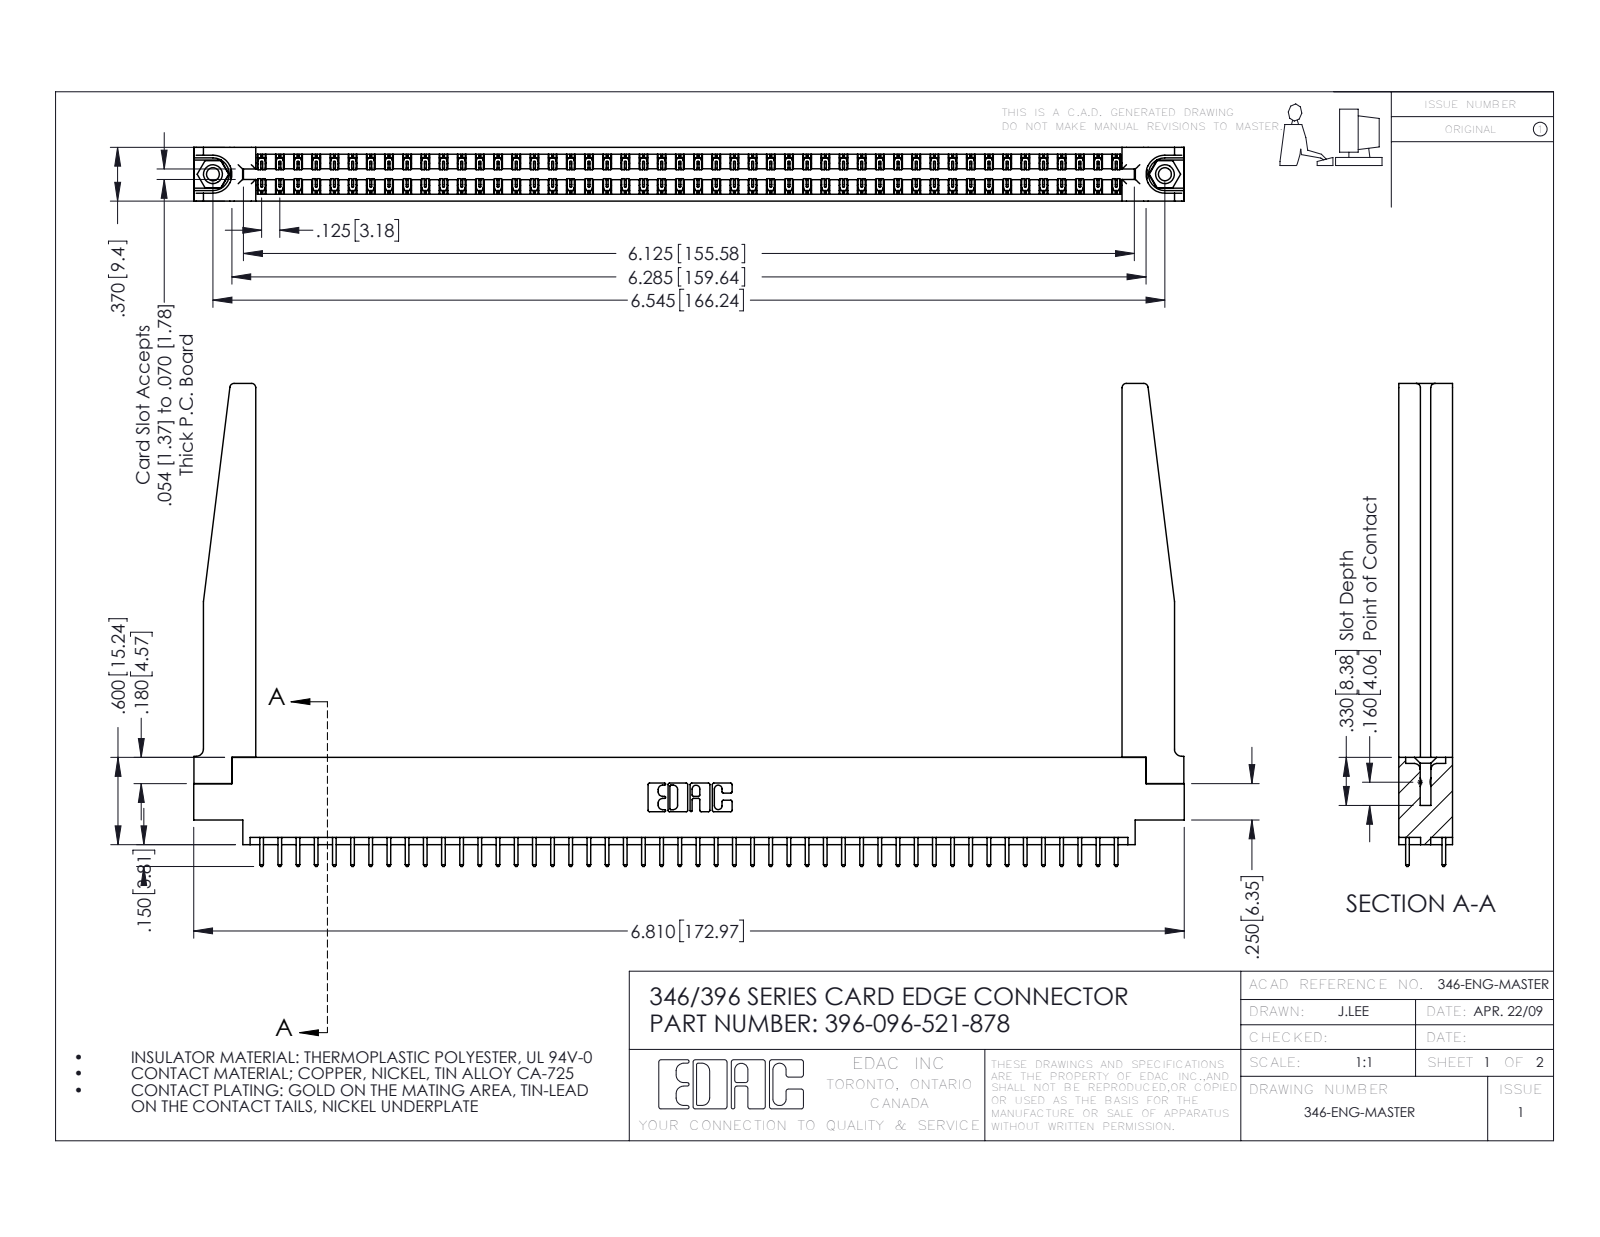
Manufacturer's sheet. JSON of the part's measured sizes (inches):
{"part_name": "346 Part_0.170 Offset - 0.156 Dia-TH; 346-220-078_345-220-078; 345-292-001_345-293-121; 345-250-001_345-250-001-102 (+1 more)", "step_written_by": "SolidWorks 2016 (CONFIG_CONTROL_DESIGN)", "units": "inches", "bodies": {"solids": 101, "faces": 5352, "planar": 3582, "cylindrical": 1718, "other": 52}, "overall_size": [6.81, 3.32, 0.37], "volume_in3": 1.442, "surface_area_in2": 45.77, "round_holes": [[0.089, 2], [0.125, 2], [0.156, 2], [0.064, 1]], "round_bosses_or_shafts": [[0.155, 2]], "partial_cylinders_radius": [[0.006, 144], [0.01, 96], [0.01, 22], [0.03, 8], [0.007, 6], [0.031, 6], [0.026, 3], [0.014, 2]], "face_to_face_distances": [0.37, 0.048, 0.322, 0.072, 0.25, 0.148, 0.15, 0.298, 0.025, 0.275], "hole_center_spacings": [0.246, 6.336, 6.545]}
